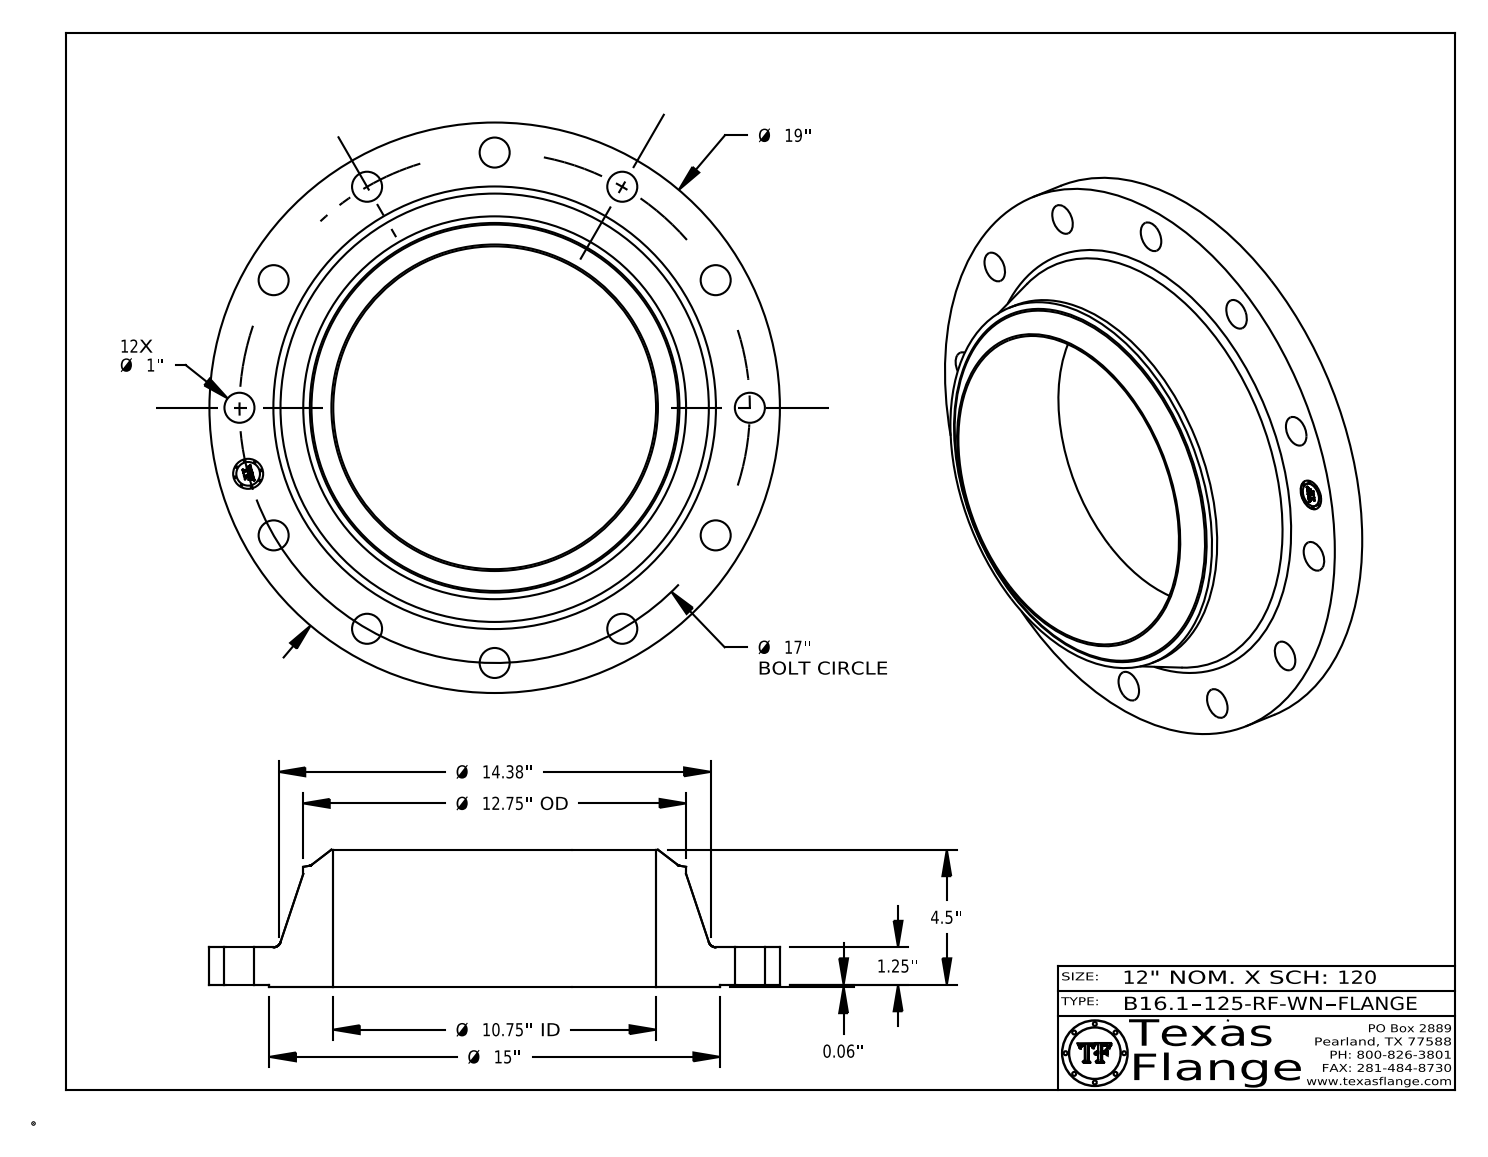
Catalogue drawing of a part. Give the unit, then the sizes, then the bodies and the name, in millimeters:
Units: millimetres
Overall size (bounding box): 482.6 × 482.6 × 115.9
Round holes (diameter × count): ⌀25.4 ×13, ⌀273.1 ×1
Round bosses / shafts (diameter × count): ⌀1.5 ×8, ⌀482.6 ×1, ⌀381 ×1, ⌀323.9 ×1, ⌀20 ×1
Main face-to-face distances: 31.8, 1.6, 33.4, 115.9, 114.3, 82.6, 0.4, 33, 31.4, 82.9
Hole centre spacings: 215.9, 417.1, 111.8, 305.3, 373.9, 111.8, 305.3, 373.9
Volume: 6 298 000 mm³ · Surface area: 473 900 mm²
Bodies: 1 solid, 431 faces (369 planar, 52 cylindrical, 10 other)
Part name (STEP PRODUCT): B16.1, Class 125-RF-WN
STEP written by: CATIA V5 STEP AP214 (AUTOMOTIVE_DESIGN)
